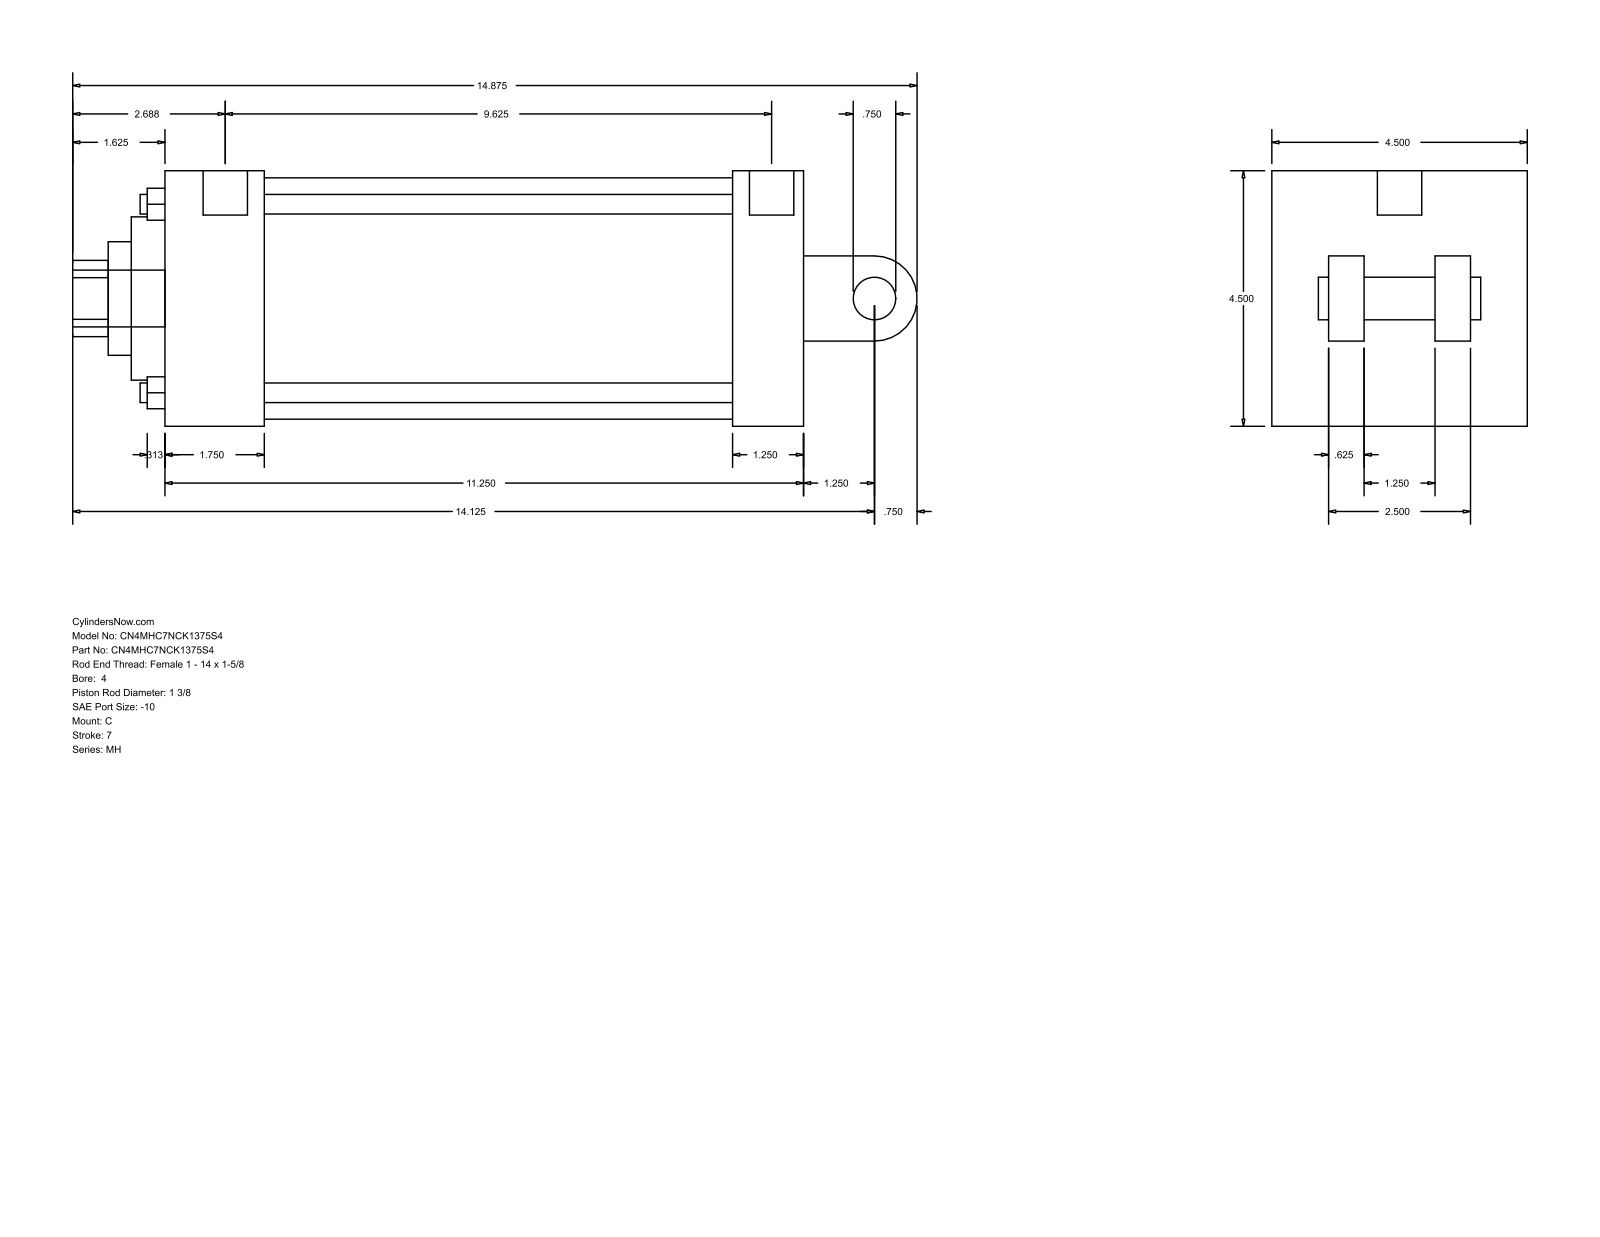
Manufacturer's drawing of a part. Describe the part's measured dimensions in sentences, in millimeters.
The part is named "MH_C__0400_1.375". Its 3-D file was written by "GSSL Pune (CONFIG_CONTROL_DESIGN)". It is 0 solids with 101 faces: 71 planar, 30 cylindrical and 0 other. Overall it measures 377.82 by 114.3 by 114.3 millimeters. Round holes: 4 of diameter 8.76, 2 of diameter 8.73, 1 of diameter 19.84, 1 of diameter 34.92, 1 of diameter 50.8, 1 of diameter 73.03, 1 of diameter 107.95. Round bosses or shafts: 2 of diameter 8.73, 1 of diameter 25.4, 1 of diameter 19.84, 1 of diameter 19.05. Partial cylindrical surfaces (rounded edges, fillets, slot ends): 1 of radius 17.06, 1 of radius 19.05. The main face-to-face distances are 114.3, 285.75, 44.45, 254, 209.55, 241.3, 31.75, 73.03, 41.27, 38.1. The hole center spacings are 59.62, 84.32, 119.25, 1.58.
